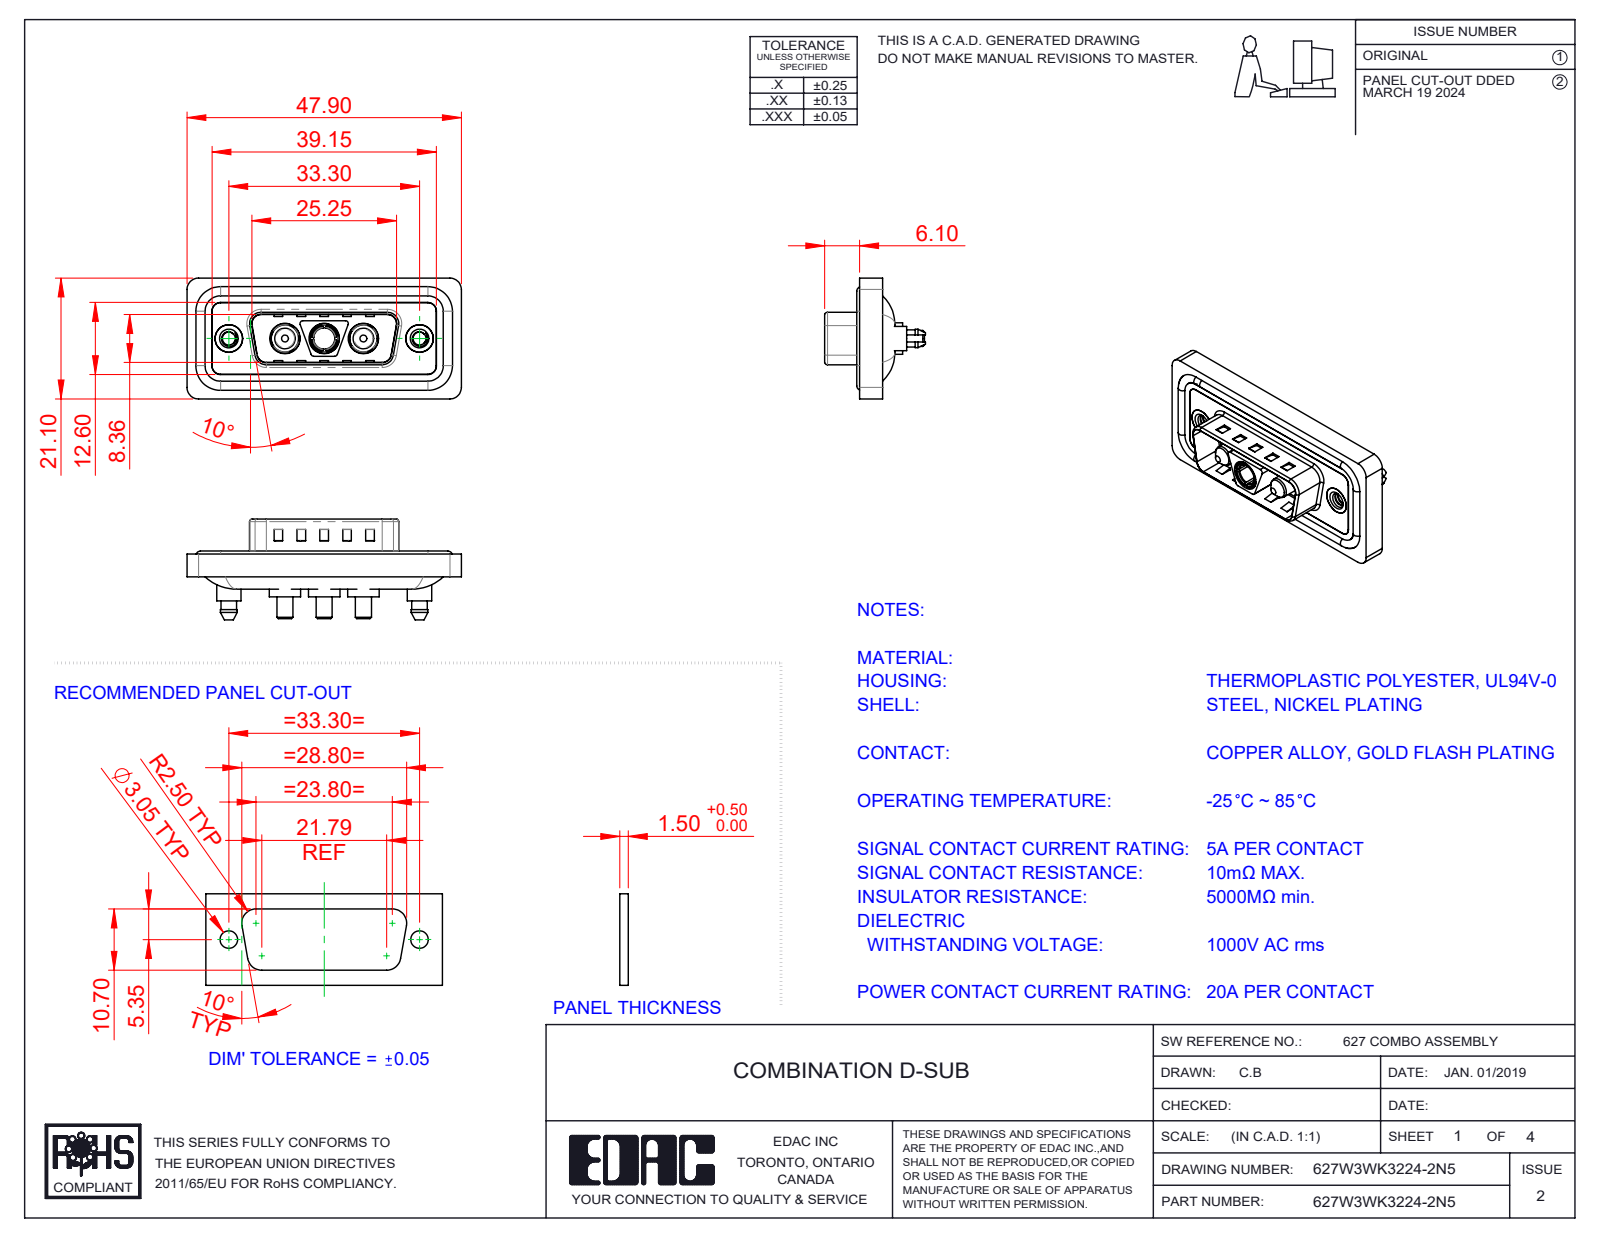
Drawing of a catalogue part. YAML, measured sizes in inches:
part_name: "Power Socket_20A S; 627Combo Housing_3WK3; 627Combo Waterproof Housing_15 Contacts; 627Combo Threaded Boardlock_5 (+4 more)"
step_written_by: "SolidWorks 2023 (CONFIG_CONTROL_DESIGN)"
units: inches
bodies: {solids: 13, faces: 659, planar: 247, cylindrical: 282, other: 130}
overall_size: [1.886, 0.831, 0.693]
volume: 0.355
surface_area: 14.66
round_holes:
  - {diameter: 0.191, count: 3}
  - {diameter: 0.209, count: 3}
  - {diameter: 0.089, count: 2}
  - {diameter: 0.157, count: 2}
  - {diameter: 0.189, count: 2}
  - {diameter: 0.197, count: 2}
  - {diameter: 0.146, count: 1}
round_bosses_or_shafts:
  - {diameter: 0.063, count: 4}
  - {diameter: 0.217, count: 3}
  - {diameter: 0.205, count: 3}
  - {diameter: 0.187, count: 3}
  - {diameter: 0.148, count: 3}
  - {diameter: 0.11, count: 3}
  - {diameter: 0.213, count: 2}
  - {diameter: 0.193, count: 2}
partial_cylinders:
  - {radius: 0.059, count: 28}
  - {radius: 0.079, count: 20}
  - {radius: 0.02, count: 12}
  - {radius: 0.063, count: 10}
  - {radius: 0.01, count: 4}
  - {radius: 0.024, count: 4}
  - {radius: 0.026, count: 4}
  - {radius: 0.035, count: 4}
face_to_face_distances: [0.016, 0.043, 0.059, 0.02, 0.063, 0.122, 0.114, 0.157, 0.028, 0.032]
hole_center_spacings: [0.27, 0.386, 0.656, 0.925, 0.539, 1.311]
